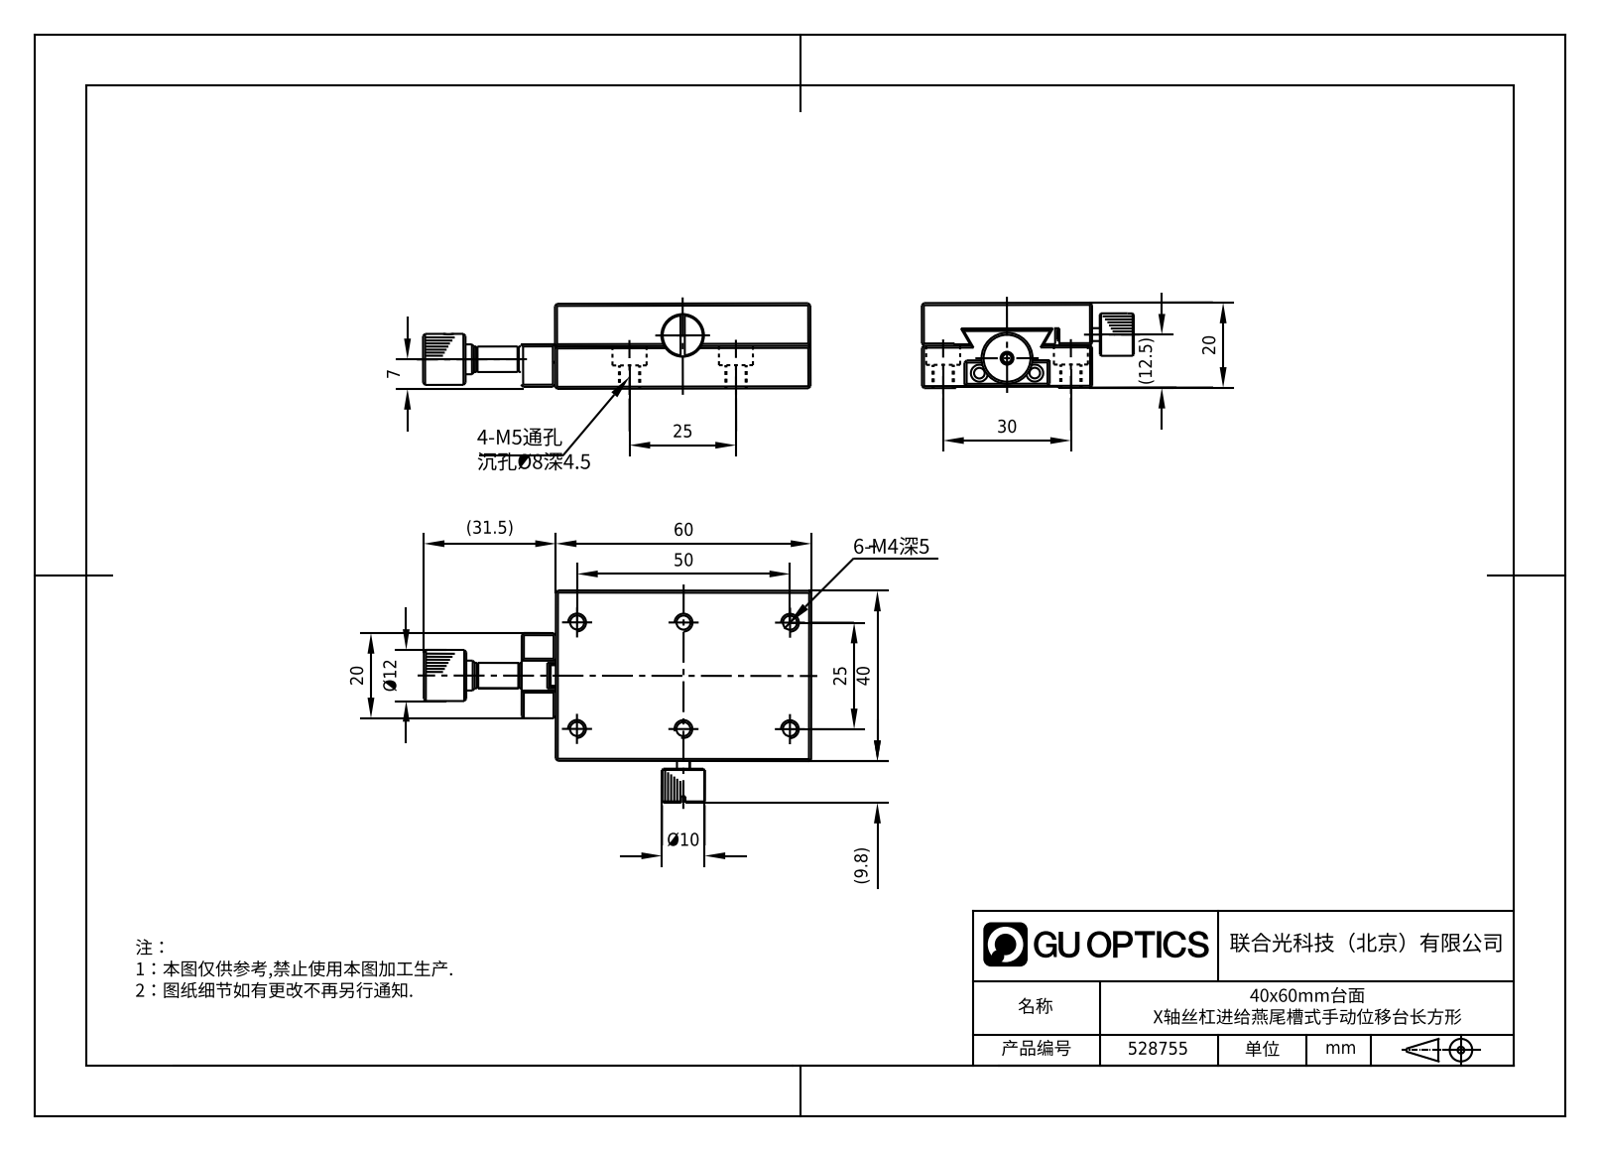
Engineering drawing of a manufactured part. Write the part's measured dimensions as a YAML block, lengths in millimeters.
part_name: "528755"
step_written_by: "SolidWorks 2020 (CONFIG_CONTROL_DESIGN)"
units: millimeters
bodies: {solids: 12, faces: 1331, planar: 813, cylindrical: 152, other: 366}
overall_size: [99.3, 51, 20]
volume: 47060
surface_area: 23096
round_holes:
  - {diameter: 2.5, count: 7}
  - {diameter: 3.3, count: 6}
  - {diameter: 4.3, count: 4}
  - {diameter: 8, count: 4}
  - {diameter: 2.05, count: 3}
  - {diameter: 5, count: 3}
  - {diameter: 2.9, count: 2}
round_bosses_or_shafts:
  - {diameter: 2.5, count: 3}
  - {diameter: 6, count: 2}
  - {diameter: 4.5, count: 2}
  - {diameter: 9, count: 1}
  - {diameter: 8, count: 1}
  - {diameter: 5, count: 1}
  - {diameter: 4, count: 1}
  - {diameter: 3, count: 1}
partial_cylinders:
  - {radius: 0.5, count: 6}
  - {radius: 3.25, count: 1}
  - {radius: 6, count: 1}
face_to_face_distances: [10, 13.7, 6, 4, 20, 9.7, 19.7, 40, 14, 6.3]
hole_center_spacings: [25, 12.75, 30.21, 10, 30, 19.53, 20, 27.95]
